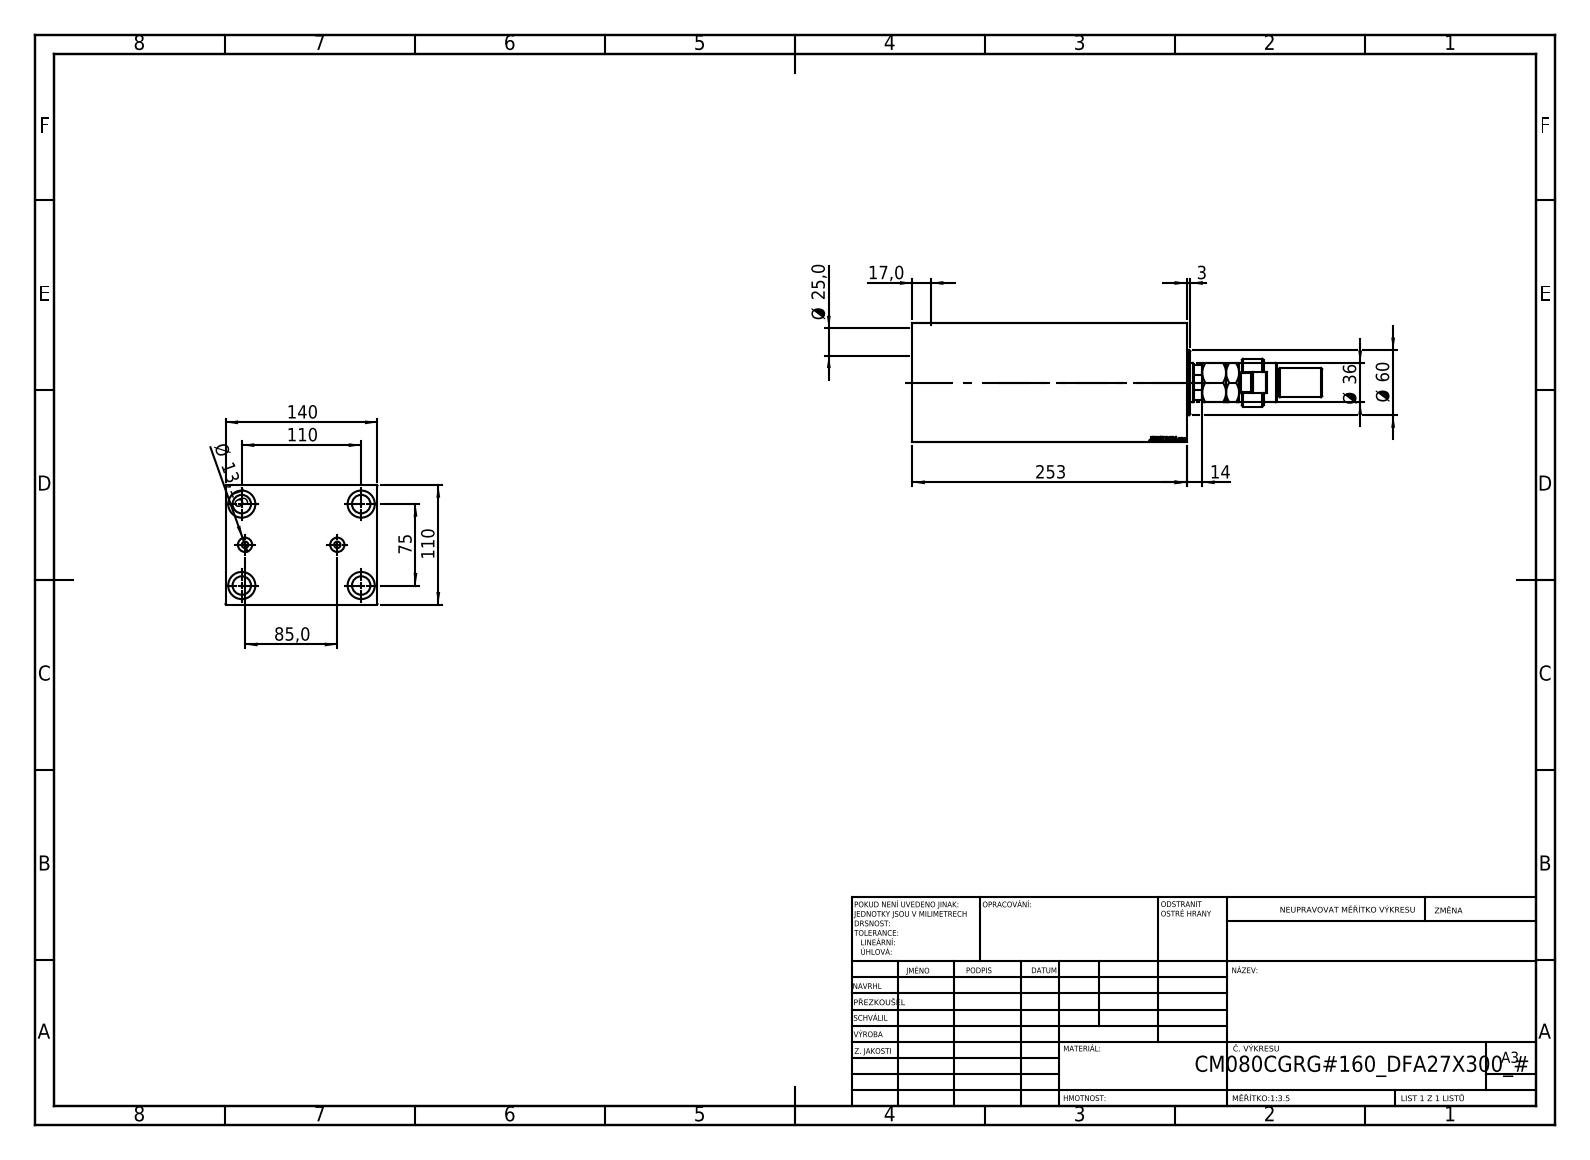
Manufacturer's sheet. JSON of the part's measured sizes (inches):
{"part_name": "V450CM_VC_B; MFA; V450CM_C_Body; V450CM_C_VCP (+1 more)", "step_written_by": "SolidWorks 2019 (CONFIG_CONTROL_DESIGN)", "units": "inches", "bodies": {"solids": 5, "faces": 945, "planar": 436, "cylindrical": 71, "other": 438}, "overall_size": [14.862, 5.512, 4.331], "volume_in3": 187.9, "surface_area_in2": 561.2, "round_holes": [[0.669, 4], [0.984, 4], [0.236, 2], [0.518, 2], [1.004, 1], [1.555, 1], [3.15, 1], [3.228, 1], [3.425, 1]], "round_bosses_or_shafts": [[2.362, 1], [1.732, 1], [1.417, 1], [1.102, 1], [1.063, 1], [0.984, 1], [0.709, 1]], "partial_cylinders_radius": [[0.374, 1], [0.591, 1], [0.689, 1]], "face_to_face_distances": [4.331, 5.512, 9.961, 9.134, 0.827, 0.551, 9.409, 8.583, 6.85, 6.299], "hole_center_spacings": [2.621, 1.481, 1.712, 2.953, 3.766, 4.331, 4.464, 5.242]}
